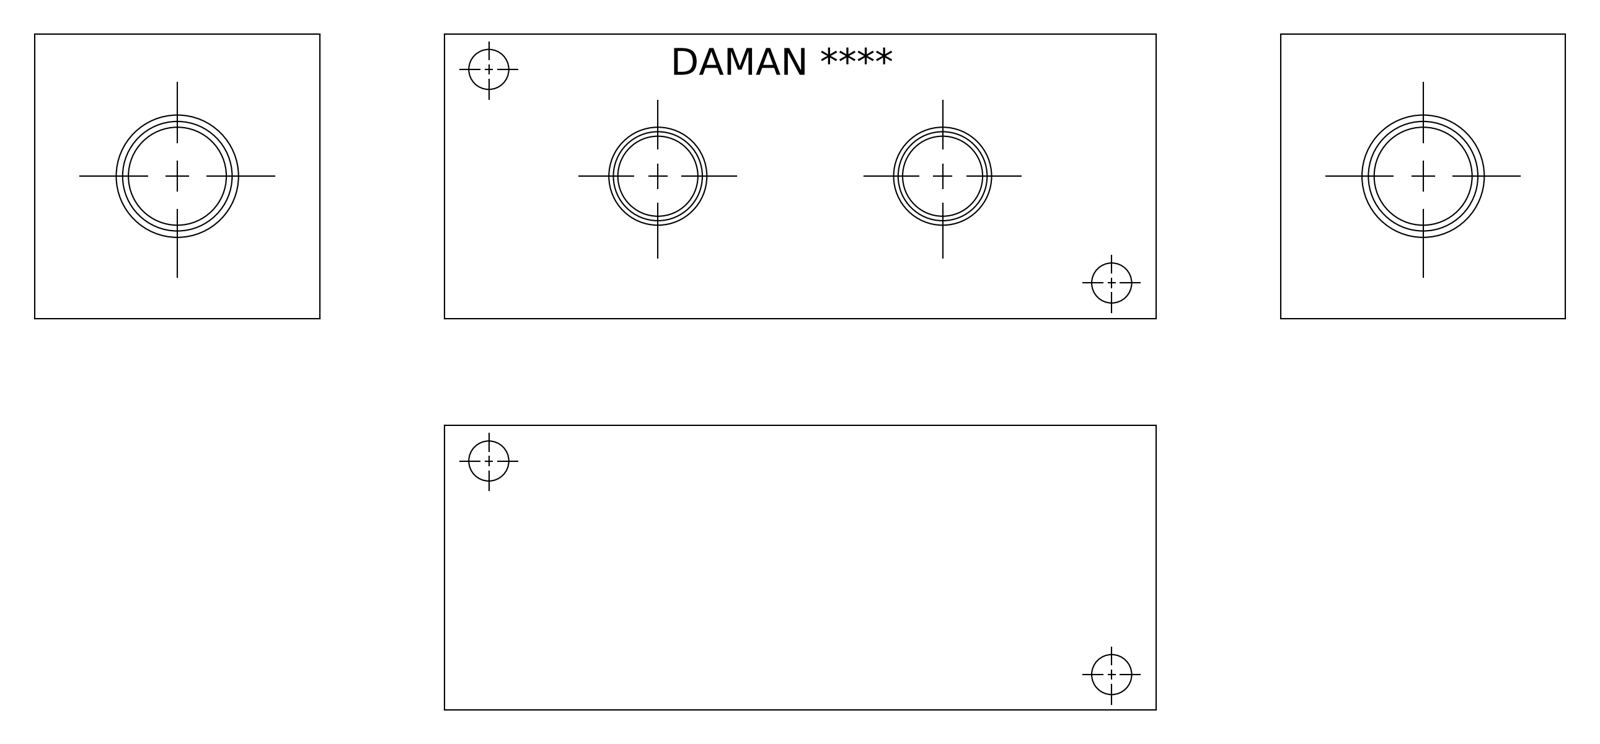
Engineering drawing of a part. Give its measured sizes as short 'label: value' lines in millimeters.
name: Part_+H0000206P_3D
written by: Autodesk Inventor 2020 (AUTOMOTIVE_DESIGN)
unit: mm
bodies: 1 solid, 334 faces (208 planar, 16 cylindrical, 110 other)
size: 127 × 50.8 × 50.8
volume: 301 702 mm³; area: 38 390 mm²
holes: 4× ⌀7.14, 2× ⌀14.3, 2× ⌀17.3, 1× ⌀17.48, 1× ⌀21.59
face distances: 50.8, 127, 15.37, 111.63, 11.73, 39.07, 96.26, 50.76, 11.69, 0.64
hole spacings: 35.69, 83.19, 117.51, 50.8
